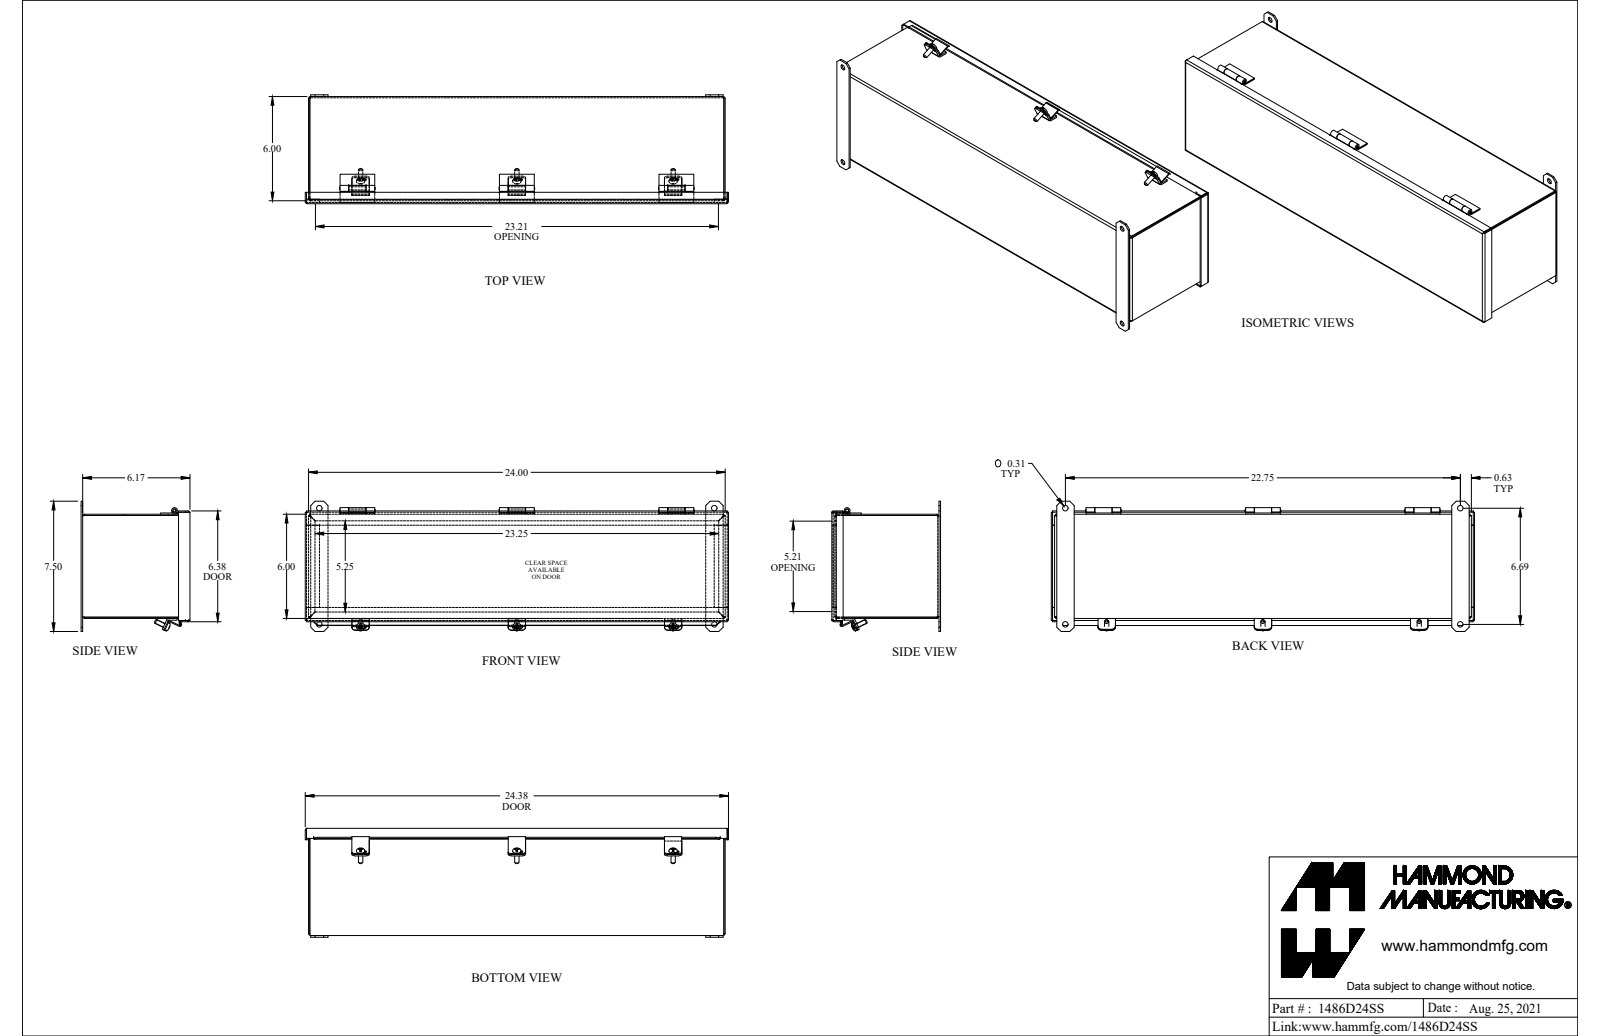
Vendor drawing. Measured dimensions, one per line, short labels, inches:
name: 1486D24SS
written by: SolidWorks 2021 (AUTOMOTIVE_DESIGN)
unit: in
bodies: 9 solids, 536 faces (346 planar, 145 cylindrical, 45 other)
size: 24.375 × 7.5 × 6.267
volume: 61.95 in³; area: 1 569 in²
holes: 4× ⌀0.313, 3× ⌀0.213, 1× ⌀0.187
bosses: 3× ⌀0.483, 3× ⌀0.25, 1× ⌀0.337, 1× ⌀0.18
rounds: 13× R0.036, 13× R0.108, 12× R0.188, 12× R0.25, 6× R0.01, 6× R0.03, 6× R0.141, 2× R0.029
face distances: 0.072, 5.928, 6.1, 5.856, 6, 6.028, 6.172, 0.187, 0.259, 23.928
hole spacings: 6.688, 9, 18, 22.75, 22.75, 23.713, 23.713
